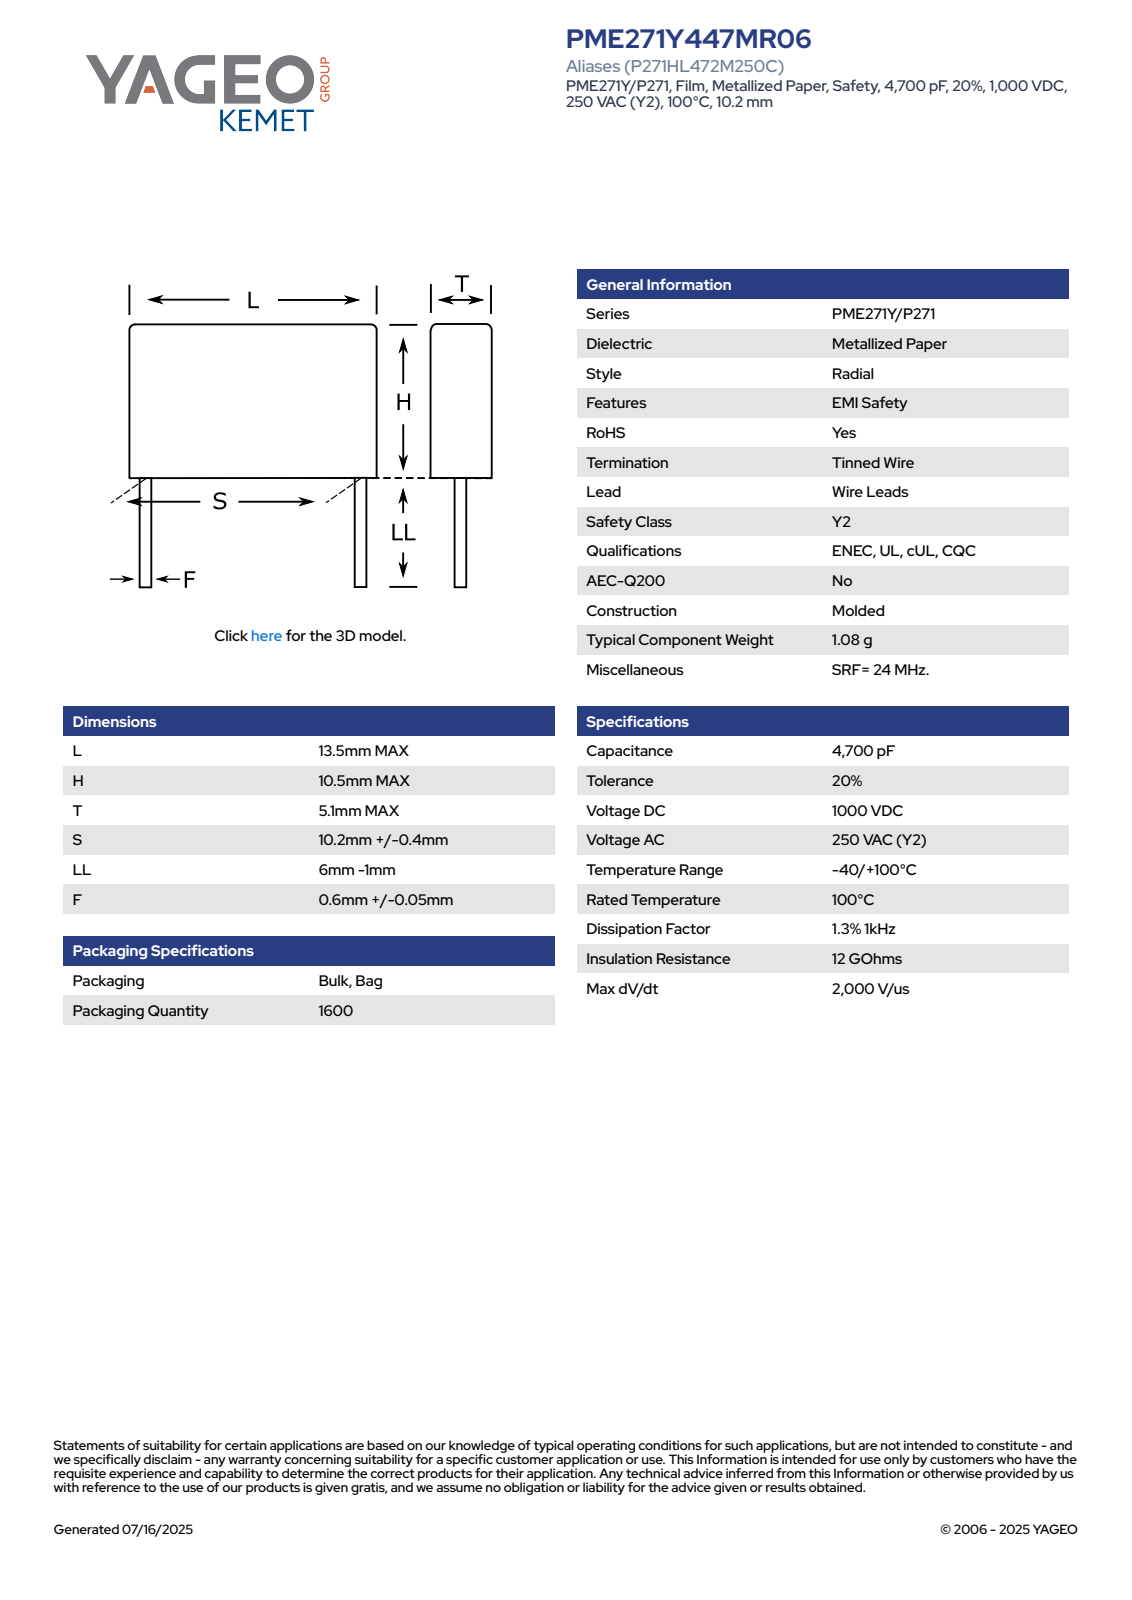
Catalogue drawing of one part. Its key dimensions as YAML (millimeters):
part_name: "CFR_MOLDED_13.5X10.5X5.1_L13.5H10.5T5.1S10.2LL5F0.65"
step_written_by: "SolidWorks 2014 (AUTOMOTIVE_DESIGN)"
units: millimeters
bodies: {solids: 4, faces: 73, planar: 65, cylindrical: 8, other: 0}
overall_size: [15.5, 13.5, 5.11]
volume: 724
surface_area: 549
round_bosses_or_shafts:
  - {diameter: 0.65, count: 2}
partial_cylinders:
  - {radius: 0.5, count: 4}
face_to_face_distances: [5.1, 10.5, 13.5, 5, 15.5, 1.21, 10.61, 5.61, 4.89, 9.4]
